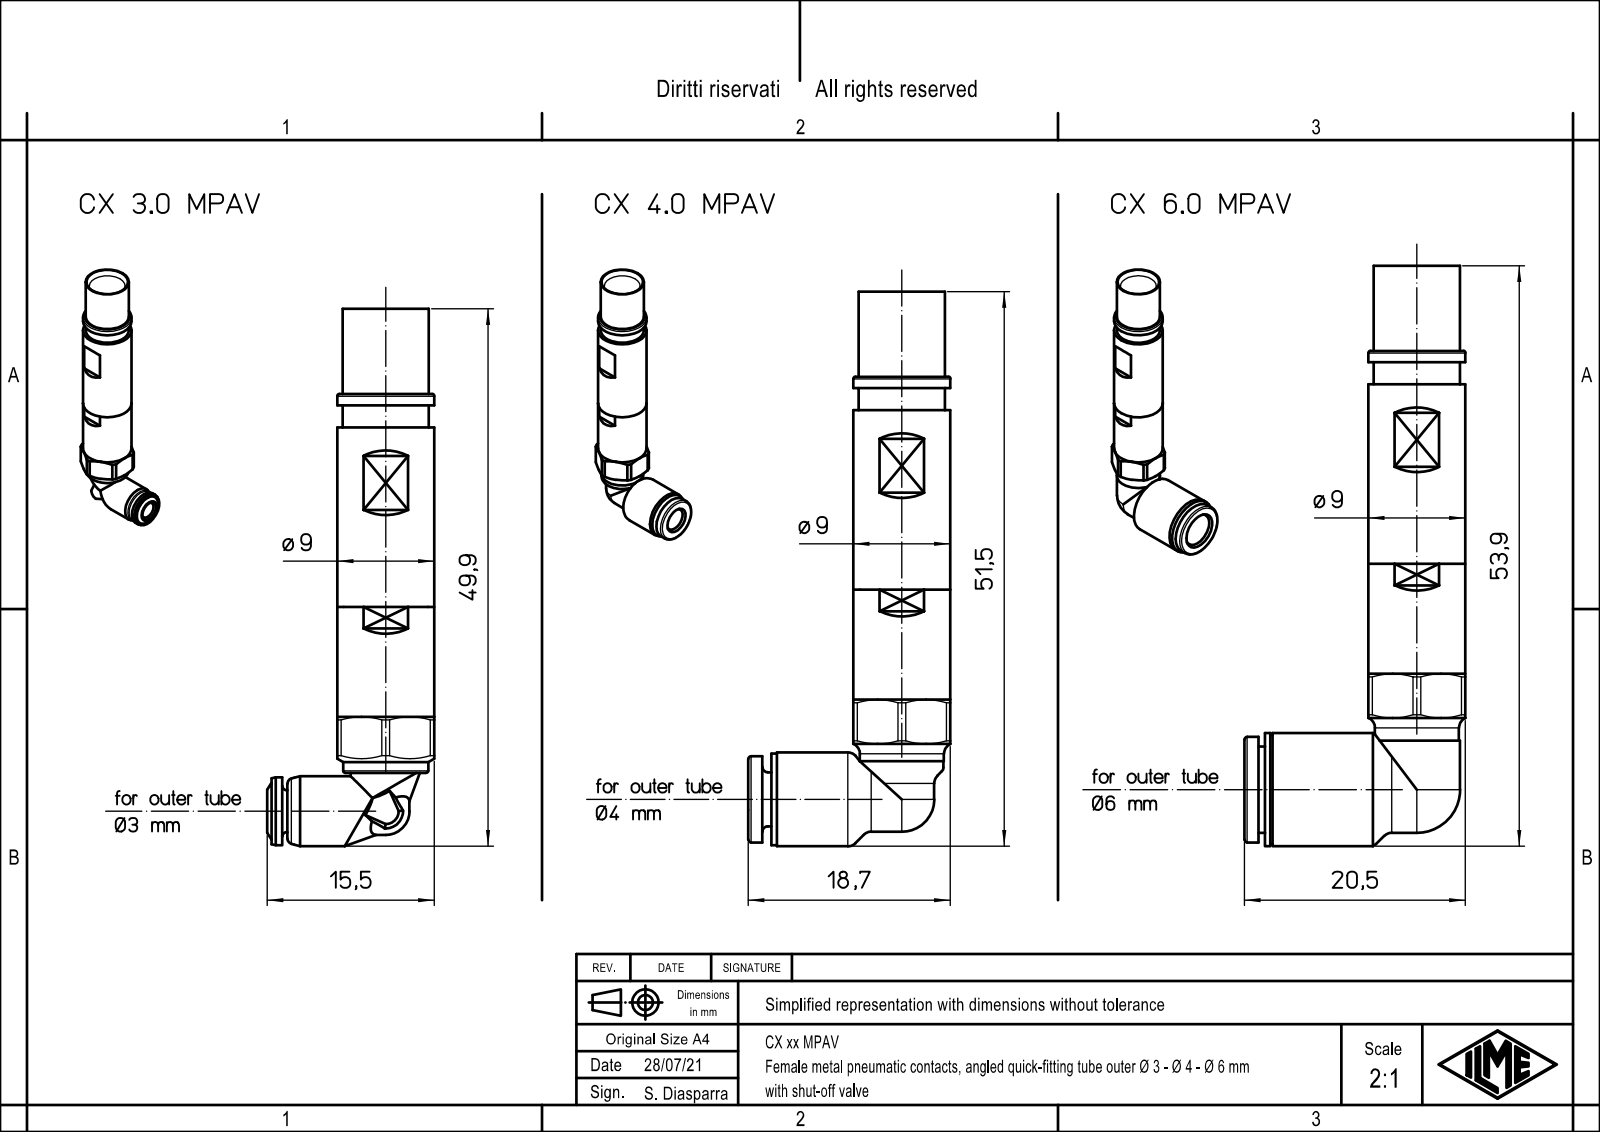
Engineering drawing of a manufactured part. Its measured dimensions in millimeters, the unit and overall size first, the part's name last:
Units: millimetres
Overall size (bounding box): 53.85 × 20.5 × 10.5
Round holes (diameter × count): ⌀6.2 ×1, ⌀6.6 ×1
Round bosses / shafts (diameter × count): ⌀8 ×2, ⌀10.5 ×1, ⌀10.1 ×1, ⌀9.8 ×1, ⌀9 ×1, ⌀7.8 ×1, ⌀4.65 ×1
Partial cylindrical surfaces — rounded edges, fillets, slot ends (radius × count): R0.14 ×1, R0.16 ×1, R0.18 ×1, R0.27 ×1, R0.5 ×1, R0.53 ×1, R5 ×1
Main face-to-face distances: 0.6, 9, 14.4, 4.2, 4.8, 3.7, 4.3, 1.3, 1.9, 11.49
Volume: 3 441 mm³ · Surface area: 2 579 mm²
Bodies: 1 solid, 160 faces (60 planar, 44 cylindrical, 56 other)
Part name (STEP PRODUCT): CX_6.0_MPAV
STEP written by: Creo Elements/Direct Modeling 20.1B 02-Apr-2019 (C) Parametric Technology GmbH (AUTOMOTIVE_DESIGN)
